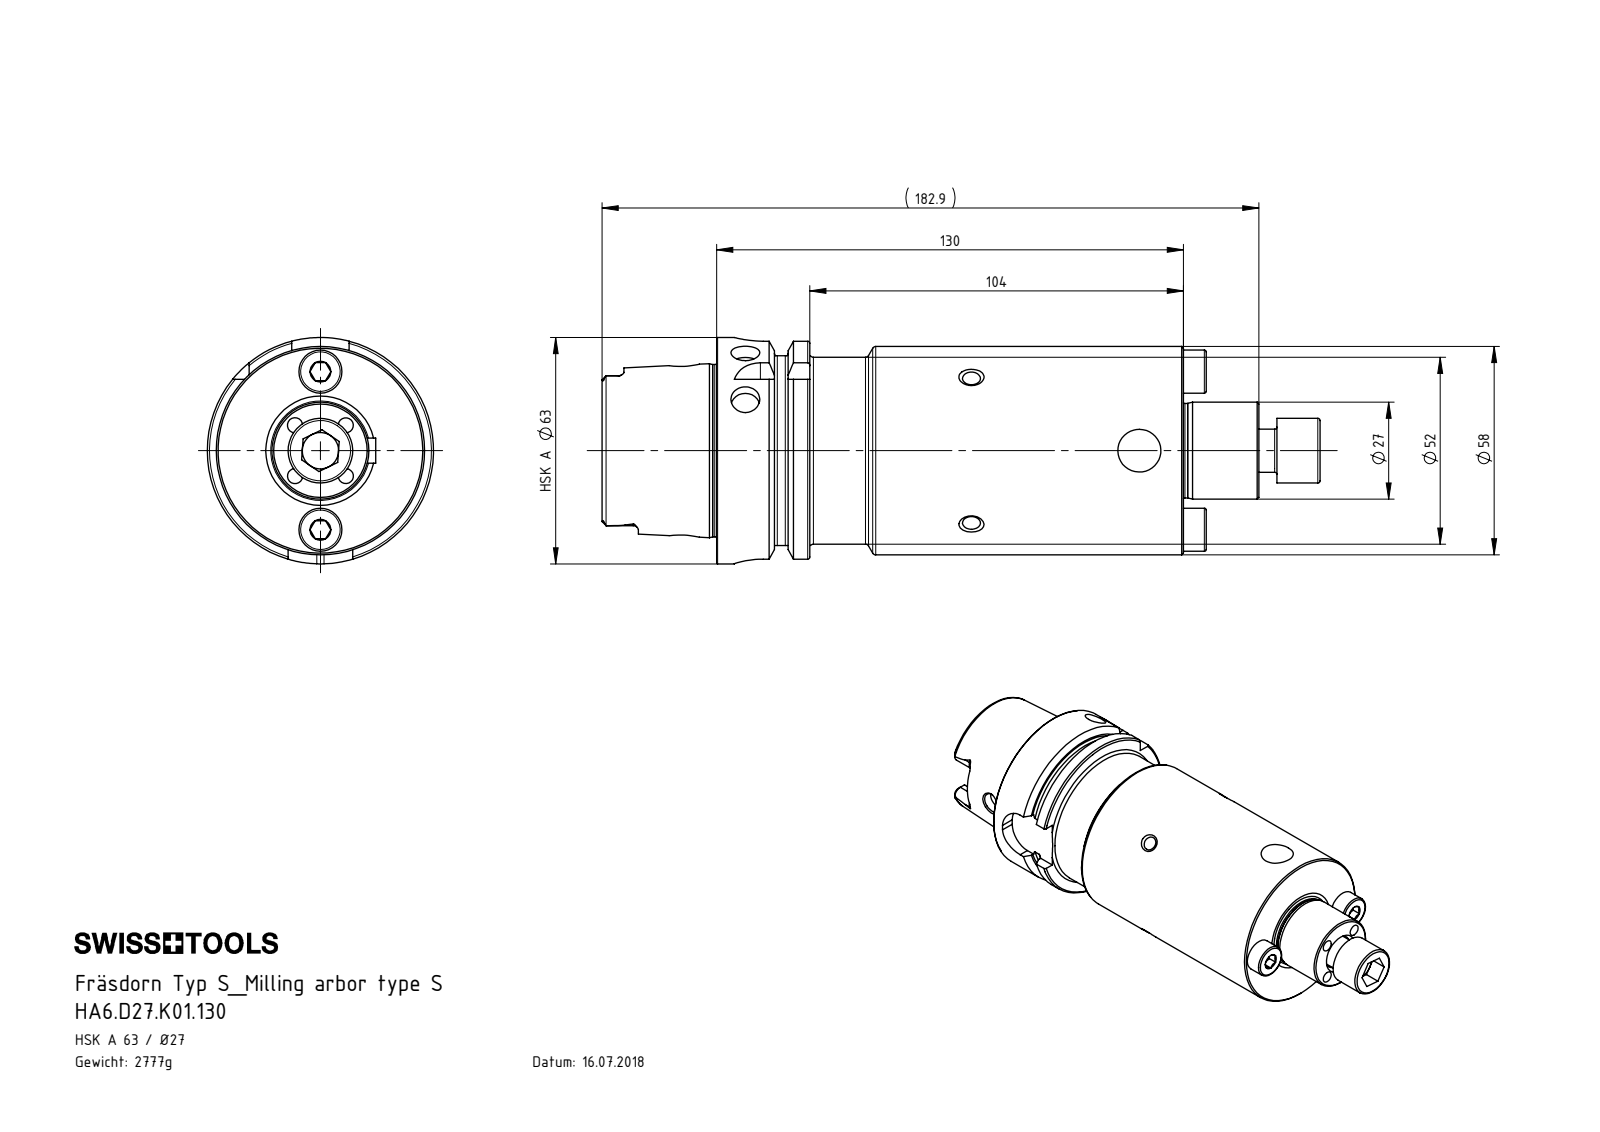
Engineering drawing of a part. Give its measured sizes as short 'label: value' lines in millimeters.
name: ISO 4762 - M12 x 30; D27-ER3.001.016_A; HA6-D27.K01.130_C_Fertigbearbeitung; D27-ER2.001.021_B (+1 more)
written by: SolidWorks 2017 (AUTOMOTIVE_DESIGN)
unit: mm
bodies: 5 solids, 391 faces (96 planar, 119 cylindrical, 176 other)
size: 199.9 × 63 × 63
volume: 353 641 mm³; area: 55 874 mm²
holes: 6× ⌀4.2, 6× ⌀5, 3× ⌀10, 2× ⌀8, 1× ⌀7.5, 1× ⌀8.4, 1× ⌀10.2, 1× ⌀13, 1× ⌀17, 1× ⌀19, 1× ⌀34, 1× ⌀40
bosses: 3× ⌀12, 2× ⌀6, 2× ⌀4.6, 1× ⌀63, 1× ⌀58, 1× ⌀54.95, 1× ⌀52, 1× ⌀47.94
rounds: 6× R1.4, 4× R2.88, 4× R8, 2× R3.5, 2× R4
face distances: 130, 16, 25.95, 104.05, 9.95, 120.05, 21, 31.9, 41.85, 57.85
hole spacings: 10, 14.14, 16.52, 29.92, 49.05, 20, 22, 44
